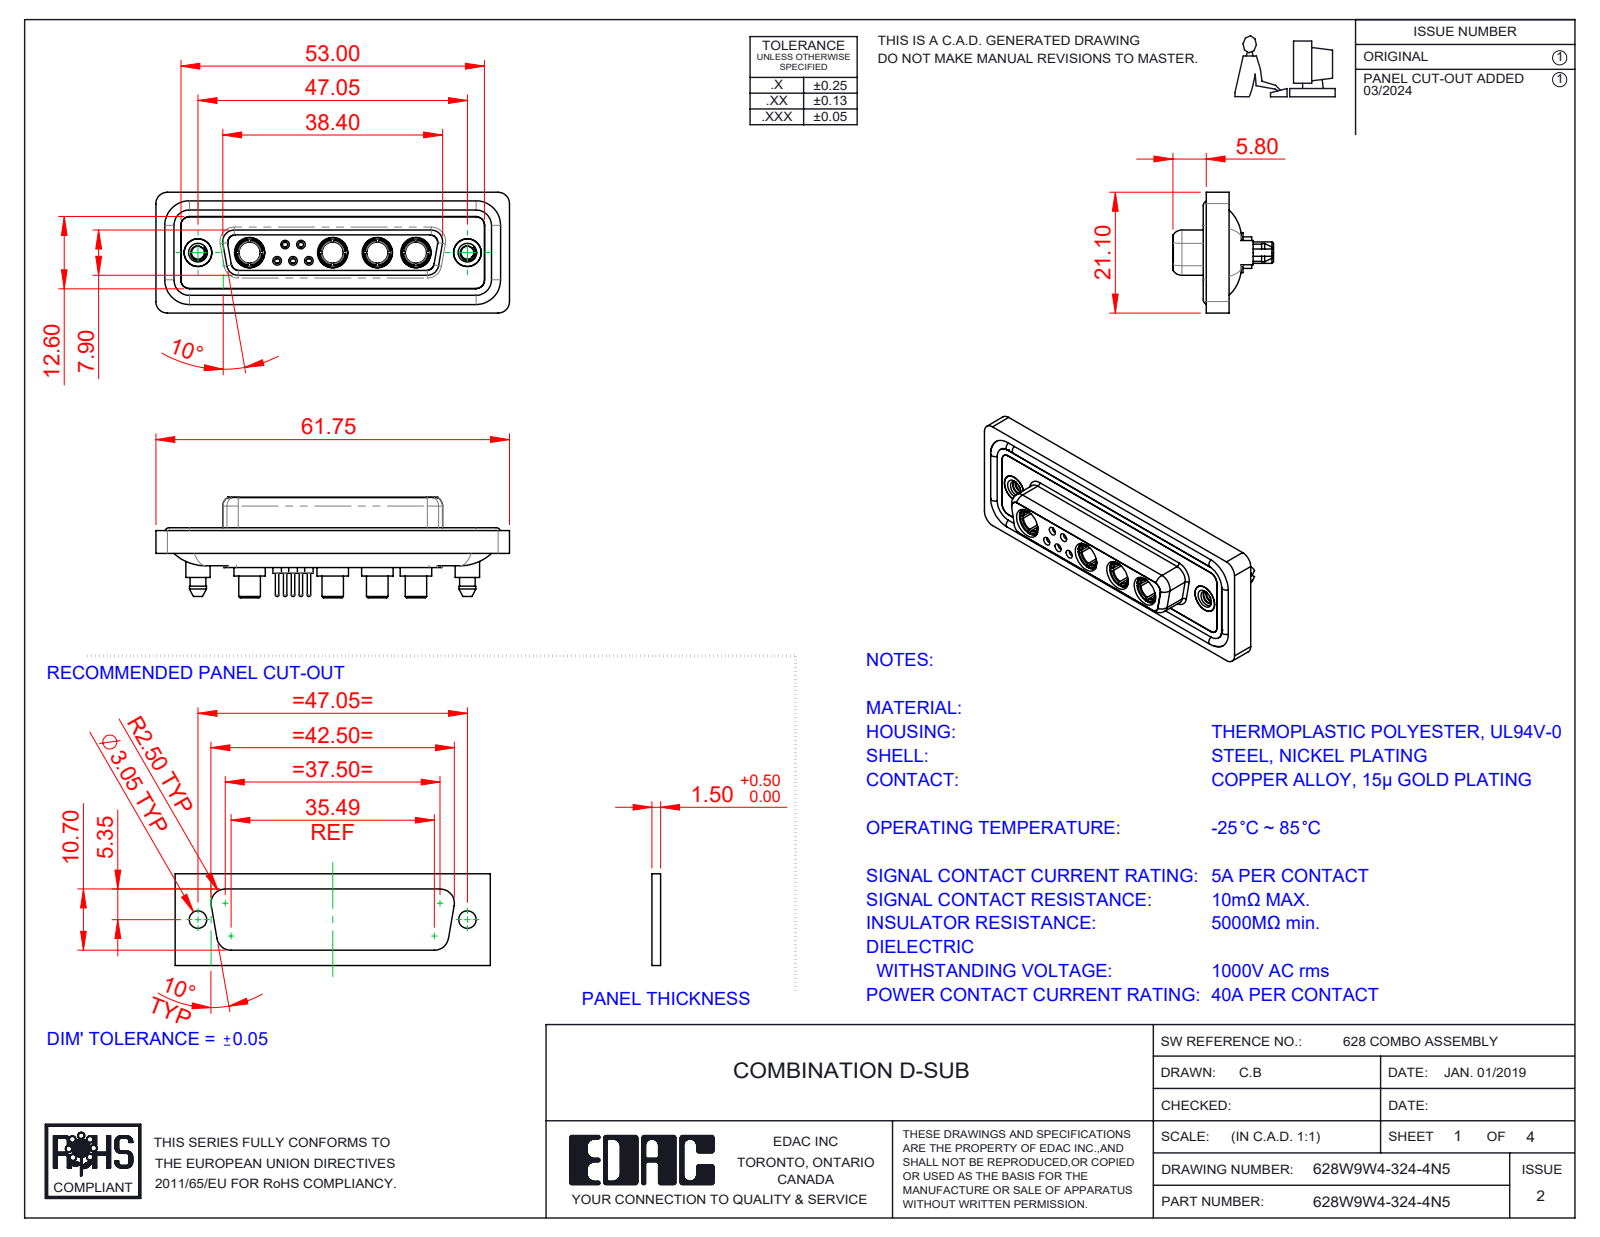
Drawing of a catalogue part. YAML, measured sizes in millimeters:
part_name: "628Combo Contact Row 1_24; 628Combo Contact Row 2_24; 628Combo Shell Rear_25 Contacts; 628Combo Waterproof Housing_25 Contacts (+5 more)"
step_written_by: "SolidWorks 2023 (CONFIG_CONTROL_DESIGN)"
units: millimeters
bodies: {solids: 20, faces: 1007, planar: 312, cylindrical: 407, other: 288}
overall_size: [61.75, 21.1, 17.55]
volume: 8431
surface_area: 13939
round_holes:
  - {diameter: 4.85, count: 6}
  - {diameter: 0.9, count: 5}
  - {diameter: 1.1, count: 5}
  - {diameter: 1.5, count: 5}
  - {diameter: 2, count: 5}
  - {diameter: 3.7, count: 4}
  - {diameter: 5.3, count: 4}
  - {diameter: 1.6, count: 3}
  - {diameter: 1.7, count: 2}
  - {diameter: 2.26, count: 2}
  - {diameter: 4, count: 2}
  - {diameter: 4.05, count: 2}
round_bosses_or_shafts:
  - {diameter: 1.6, count: 6}
  - {diameter: 2.2, count: 5}
  - {diameter: 0.6, count: 5}
  - {diameter: 5.5, count: 4}
  - {diameter: 5.2, count: 4}
  - {diameter: 4.96, count: 4}
  - {diameter: 4.75, count: 4}
  - {diameter: 3.75, count: 4}
partial_cylinders:
  - {radius: 1.5, count: 24}
  - {radius: 2, count: 18}
  - {radius: 1.6, count: 10}
  - {radius: 1.35, count: 8}
  - {radius: 0.25, count: 4}
  - {radius: 0.5, count: 4}
  - {radius: 0.6, count: 4}
  - {radius: 0.65, count: 4}
face_to_face_distances: [0.4, 1.8, 7.45, 5.65, 0.5, 7.05, 6.6, 1.6, 1.1, 2.9]
hole_center_spacings: [3.16, 2.77, 5.03, 2.76, 4.4, 5.02, 5.54, 5.73]
